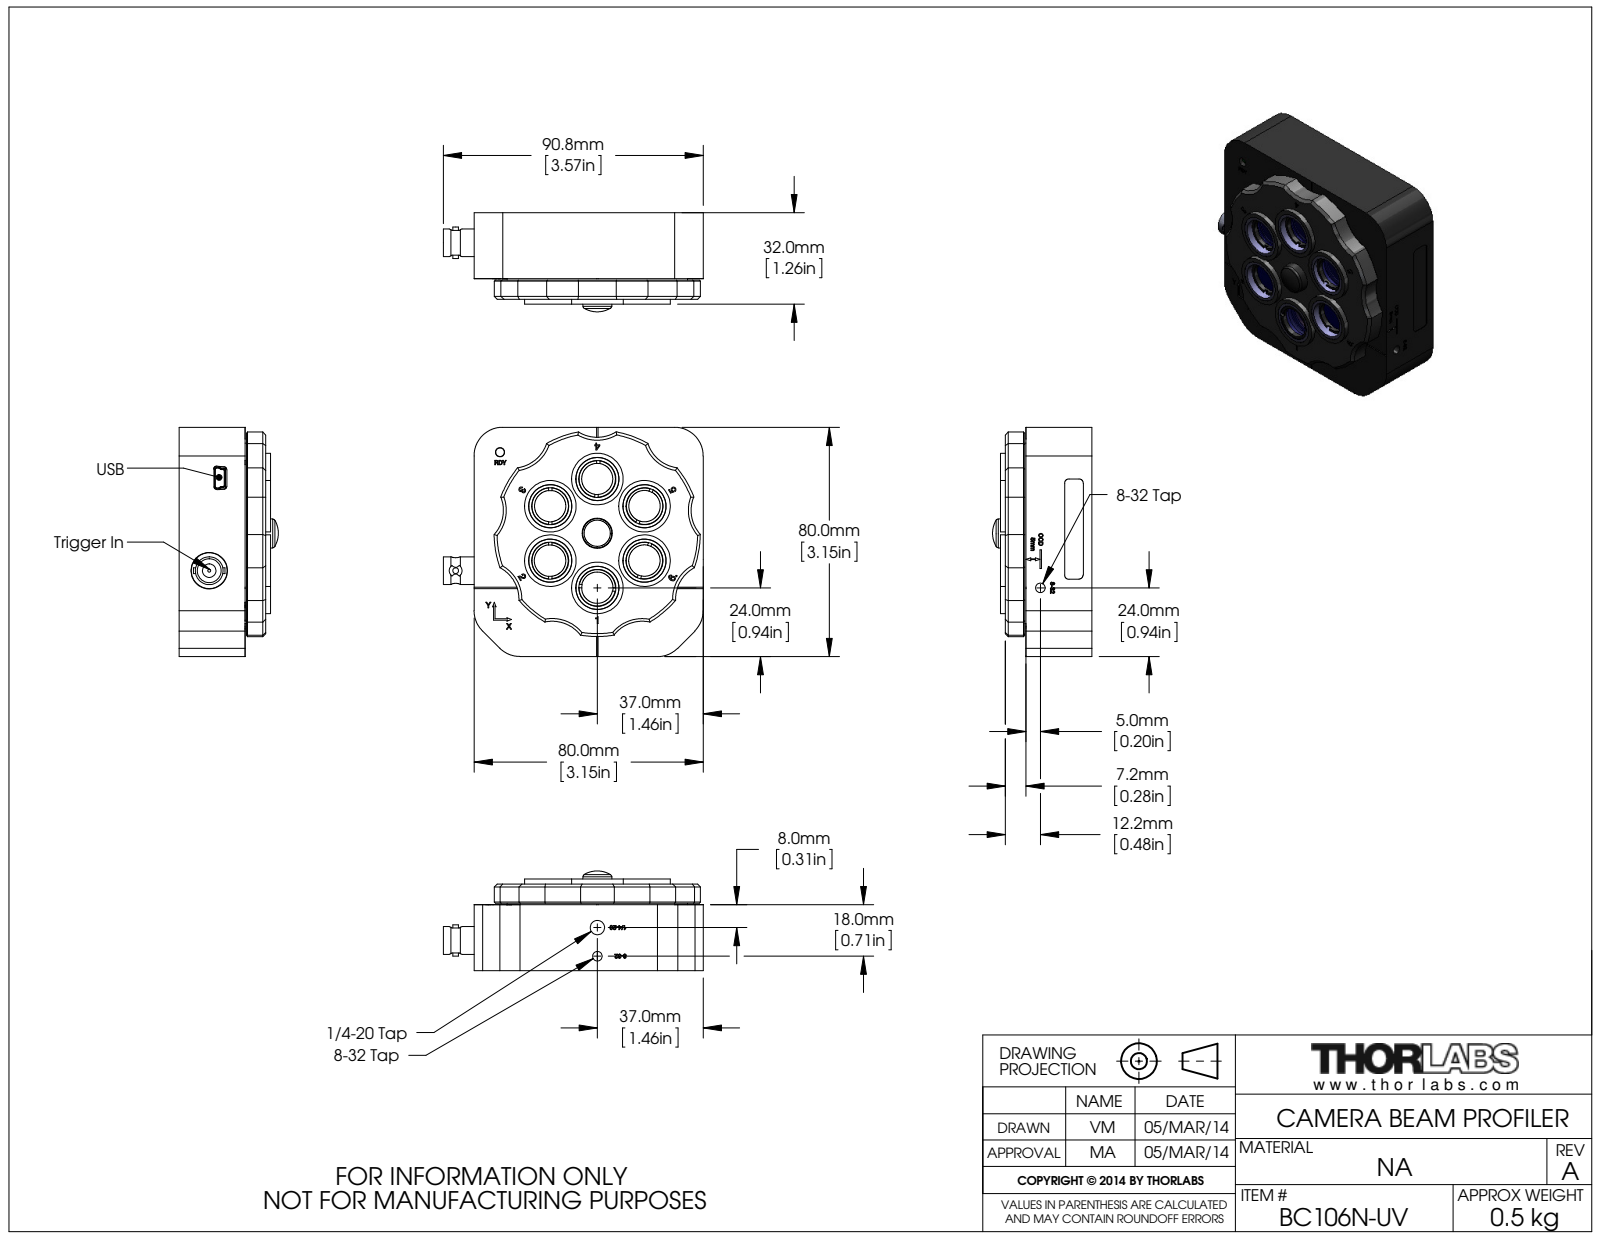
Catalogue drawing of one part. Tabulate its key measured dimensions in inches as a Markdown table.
| quantity | value |
| --- | --- |
| part name | M0092-0817-0b Trägerrad Filter mit 6xSM05 Teil2 BC110_mit Laserbeschriftung; Telegärtner J01001B0615_Standard; M0092-0816-0a Trägerrad Filter mit 6xSM05 Teil1 BC110_Standard; Trägerrad Filter mit 6xSM05 BC110 Baugruppe (+8 more) |
| STEP written by | SolidWorks 2013 (AUTOMOTIVE_DESIGN) |
| units | inches |
| bodies | 35 solids, 3683 faces (2342 planar, 528 cylindrical, 813 other) |
| overall size | 3.575 × 3.15 × 1.366 |
| volume | 5.554 in³ |
| surface area | 131.9 in² |
| round holes (diameter × count) | 0.063 × 18, 0.087 × 10, 0.551 × 7, 0.159 × 6, 0.43 × 6, 0.453 × 6, 0.508 × 6, 0.593 × 6, 0.091 × 4, 0.098 × 3, 0.13 × 3, 0.197 × 3 |
| round bosses / shafts (diameter × count) | 0.591 × 7, 0.079 × 7, 0.709 × 6, 0.535 × 6, 0.5 × 6, 0.157 × 6, 0.15 × 6, 0.118 × 6 |
| partial cylindrical surfaces (radius × count) | 0.118 × 22, 0.098 × 14, 0.039 × 12, 0.492 × 9, 0.012 × 8, 0.028 × 8, 0.059 × 8, 0.354 × 8 |
| main face-to-face distances | 0.059, 0.835, 0.894, 0.193, 0.094, 0.252, 1.028, 1.087, 0.079, 0.189 |
| hole center spacings | 0.984, 0.503, 0.748, 1.236, 1.705, 0.88, 1.147, 1.674 |
